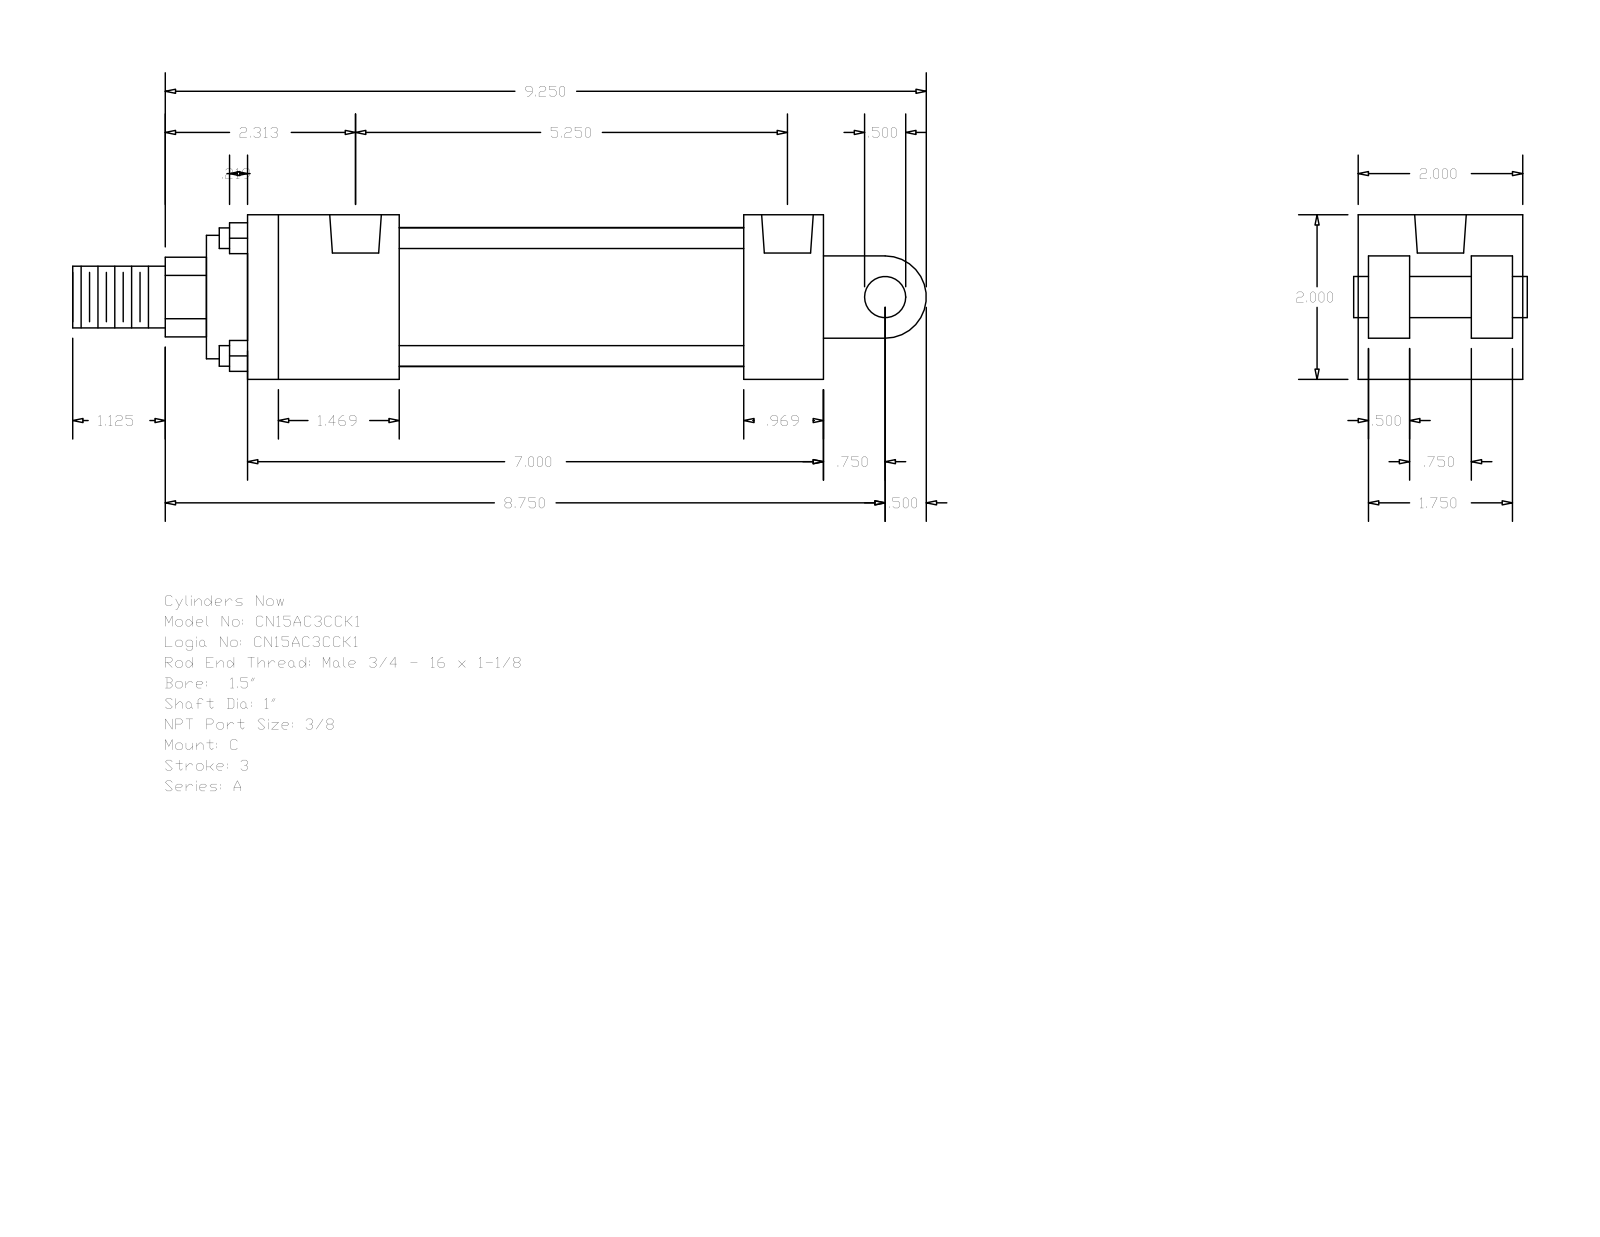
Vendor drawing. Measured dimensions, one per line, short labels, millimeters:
name: A_C__0150_1
written by: GSSL Pune (CONFIG_CONTROL_DESIGN)
unit: mm
bodies: 0 solids, 99 faces (70 planar, 29 cylindrical, 0 other)
size: 263.52 × 50.8 × 50.8
holes: 4× ⌀5.56, 2× ⌀15.93
bosses: 4× ⌀6.35, 1× ⌀42.93, 1× ⌀38.1, 1× ⌀25.4, 1× ⌀19.05, 1× ⌀12.7
rounds: 1× R12.29, 1× R12.7
face distances: 50.8, 12.7, 3.17, 15.87, 47.63, 34.93, 31.76, 177.8, 38.1, 153.19
hole spacings: 3.97, 125.41, 129.38, 133.35
